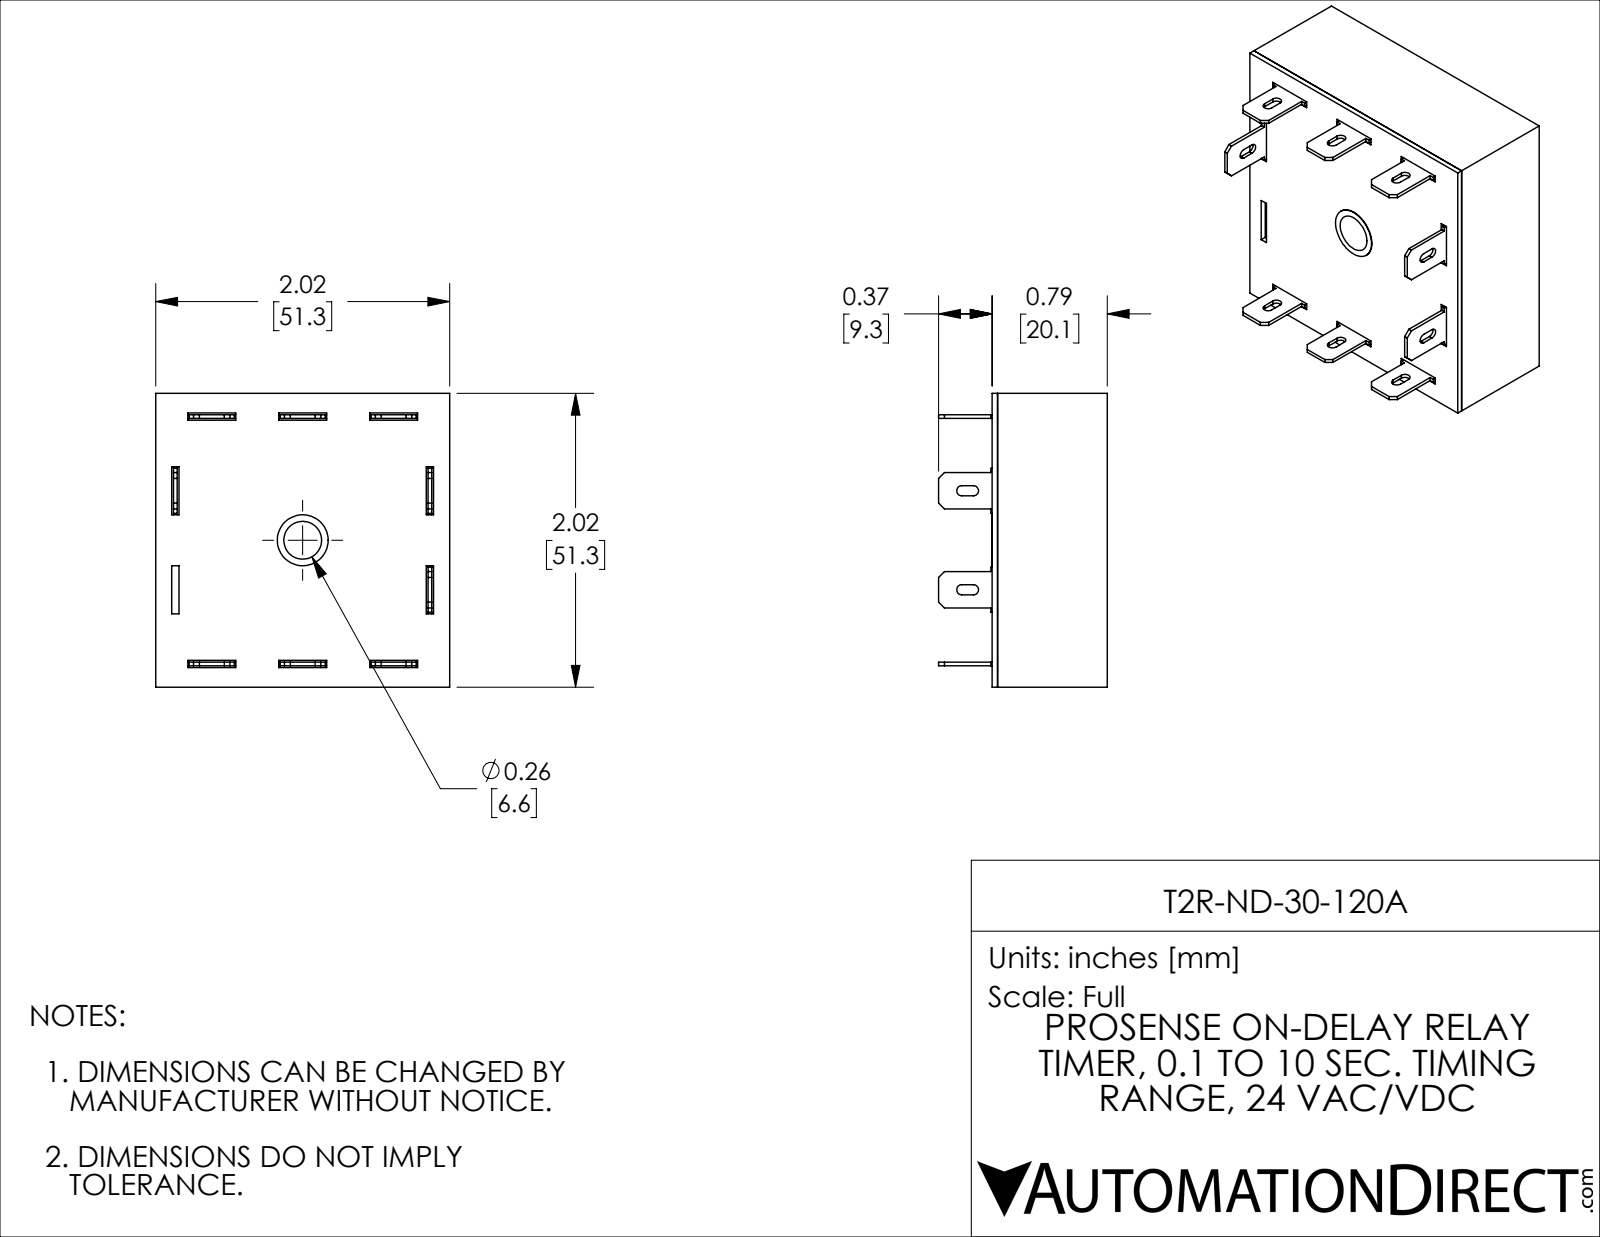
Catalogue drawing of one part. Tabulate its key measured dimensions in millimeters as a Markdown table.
| quantity | value |
| --- | --- |
| part name | T2R-ND-30-120A |
| STEP written by | SolidWorks 2021 (CONFIG_CONTROL_DESIGN) |
| units | millimeters |
| bodies | 11 solids, 280 faces (256 planar, 22 cylindrical, 2 other) |
| overall size | 51.31 × 51.31 × 29.46 |
| volume | 11 178 mm³ |
| surface area | 23 301 mm² |
| round holes (diameter × count) | 8.89 × 1 |
| partial cylindrical surfaces (radius × count) | 0.89 × 10 |
| main face-to-face distances | 1.14, 50.16, 19.15, 20.12, 0.97, 18.01, 18.98, 51.3, 3.74, 47.56 |
